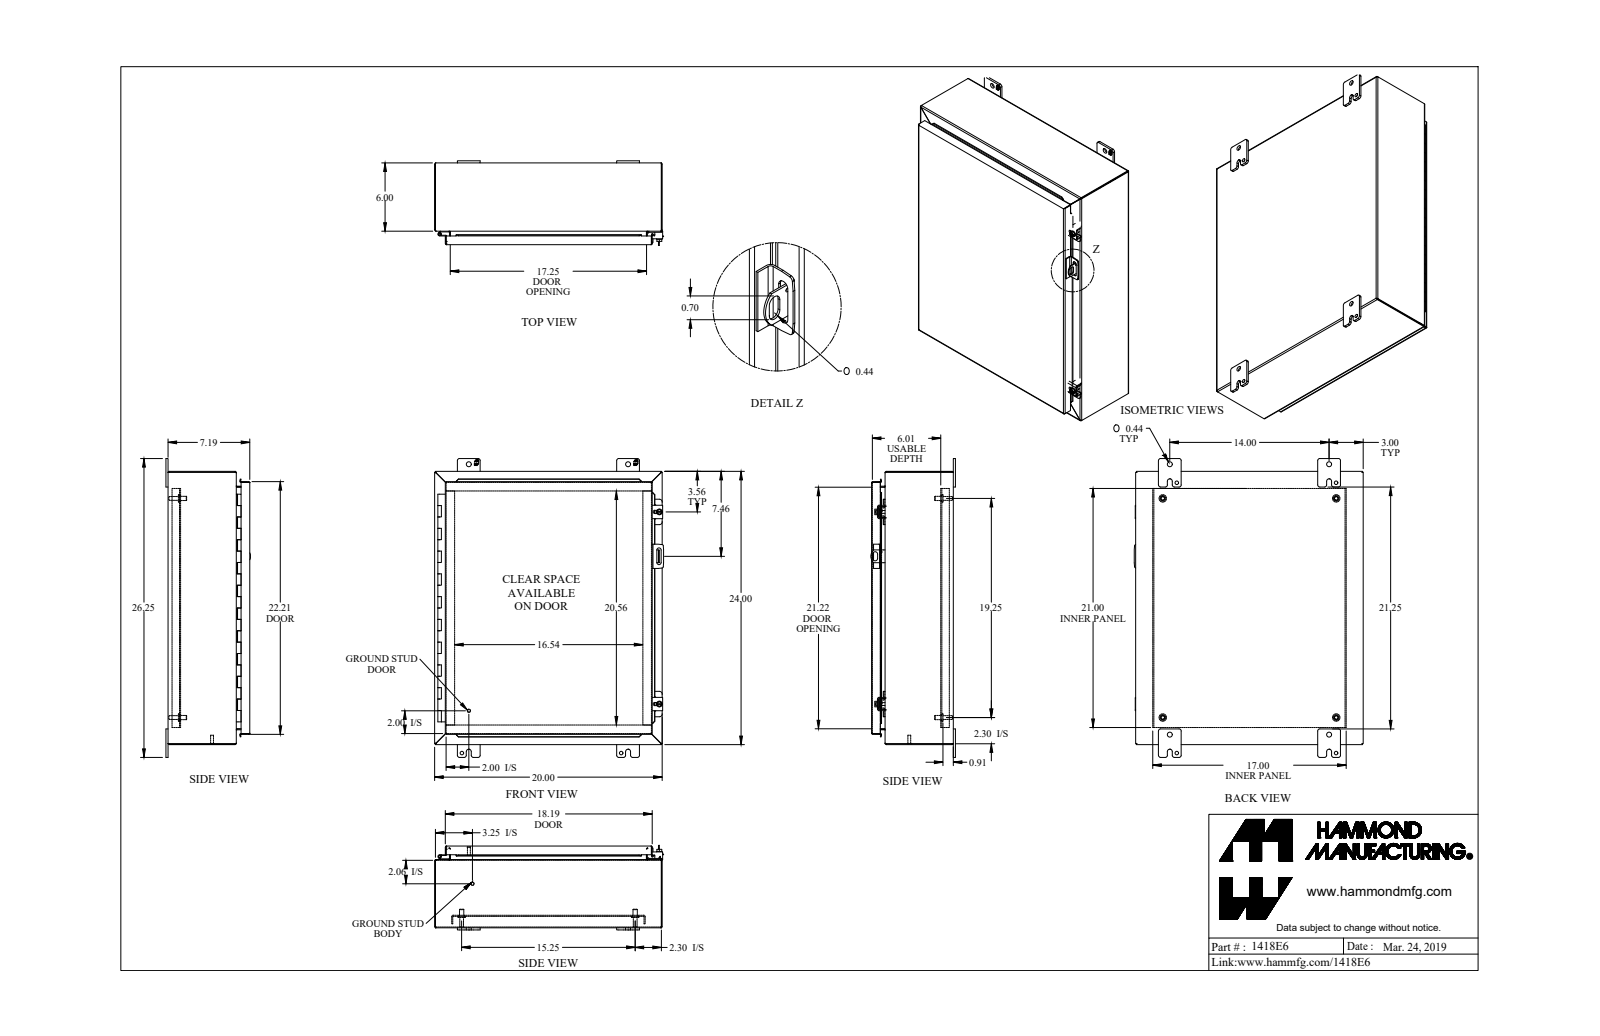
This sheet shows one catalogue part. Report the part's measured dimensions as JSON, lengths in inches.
{"part_name": "1418E6", "step_written_by": "SolidWorks 2019 (AUTOMOTIVE_DESIGN)", "units": "inches", "bodies": {"solids": 37, "faces": 949, "planar": 668, "cylindrical": 239, "other": 42}, "overall_size": [26.25, 20.125, 7.437], "volume_in3": 449.4, "surface_area_in2": 4381, "round_holes": [[0.313, 4], [0.437, 4], [0.5, 4], [0.213, 2], [0.265, 2], [0.307, 2], [0.375, 2], [0.445, 2], [0.125, 1], [0.187, 1]], "round_bosses_or_shafts": [[0.65, 4], [0.375, 4], [0.33, 4], [1, 2], [0.5, 2], [0.39, 2], [0.281, 2], [0.25, 2]], "partial_cylinders_radius": [[0.188, 26], [0.036, 16], [0.108, 16], [0.048, 13], [0.143, 13], [0.079, 8], [0.218, 8], [0.25, 8]], "face_to_face_distances": [0.072, 7.113, 7.185, 0.767, 6.346, 6.418, 0.095, 0.937, 1.009, 6.081], "hole_center_spacings": [24.559, 1.735, 14, 15.25, 23.75, 27.569, 1.625, 2.434]}
